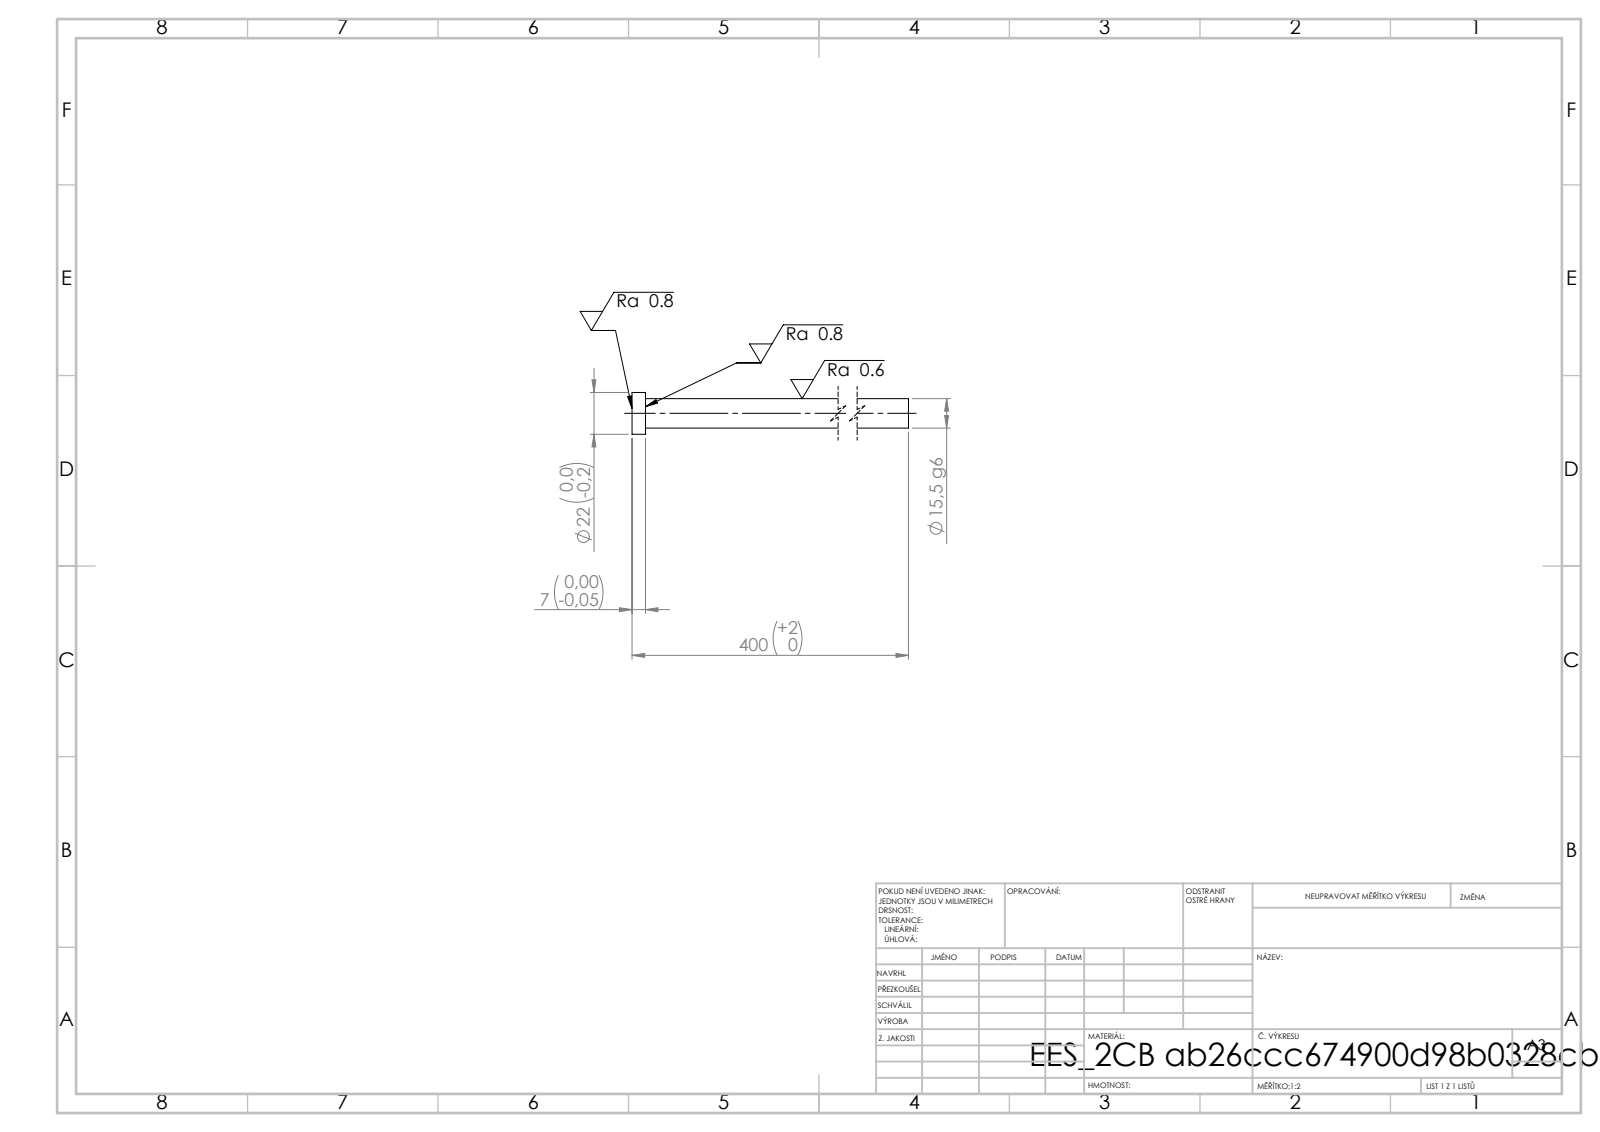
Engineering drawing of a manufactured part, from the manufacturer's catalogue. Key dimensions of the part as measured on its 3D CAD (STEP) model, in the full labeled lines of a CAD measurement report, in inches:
STEP written by: SolidWorks 2019 (CONFIG_CONTROL_DESIGN)
Units: inches
Bodies: 1 solid, 7 faces (3 planar, 4 cylindrical, 0 other)
Overall size (bounding box): 15.748 × 0.866 × 0.866
Volume: 4.688 in³ · Surface area: 31.59 in²
Round bosses / shafts (diameter × count): ⌀0.866 ×1, ⌀0.61 ×1
Main face-to-face distances: 0.276, 15.748, 15.472
